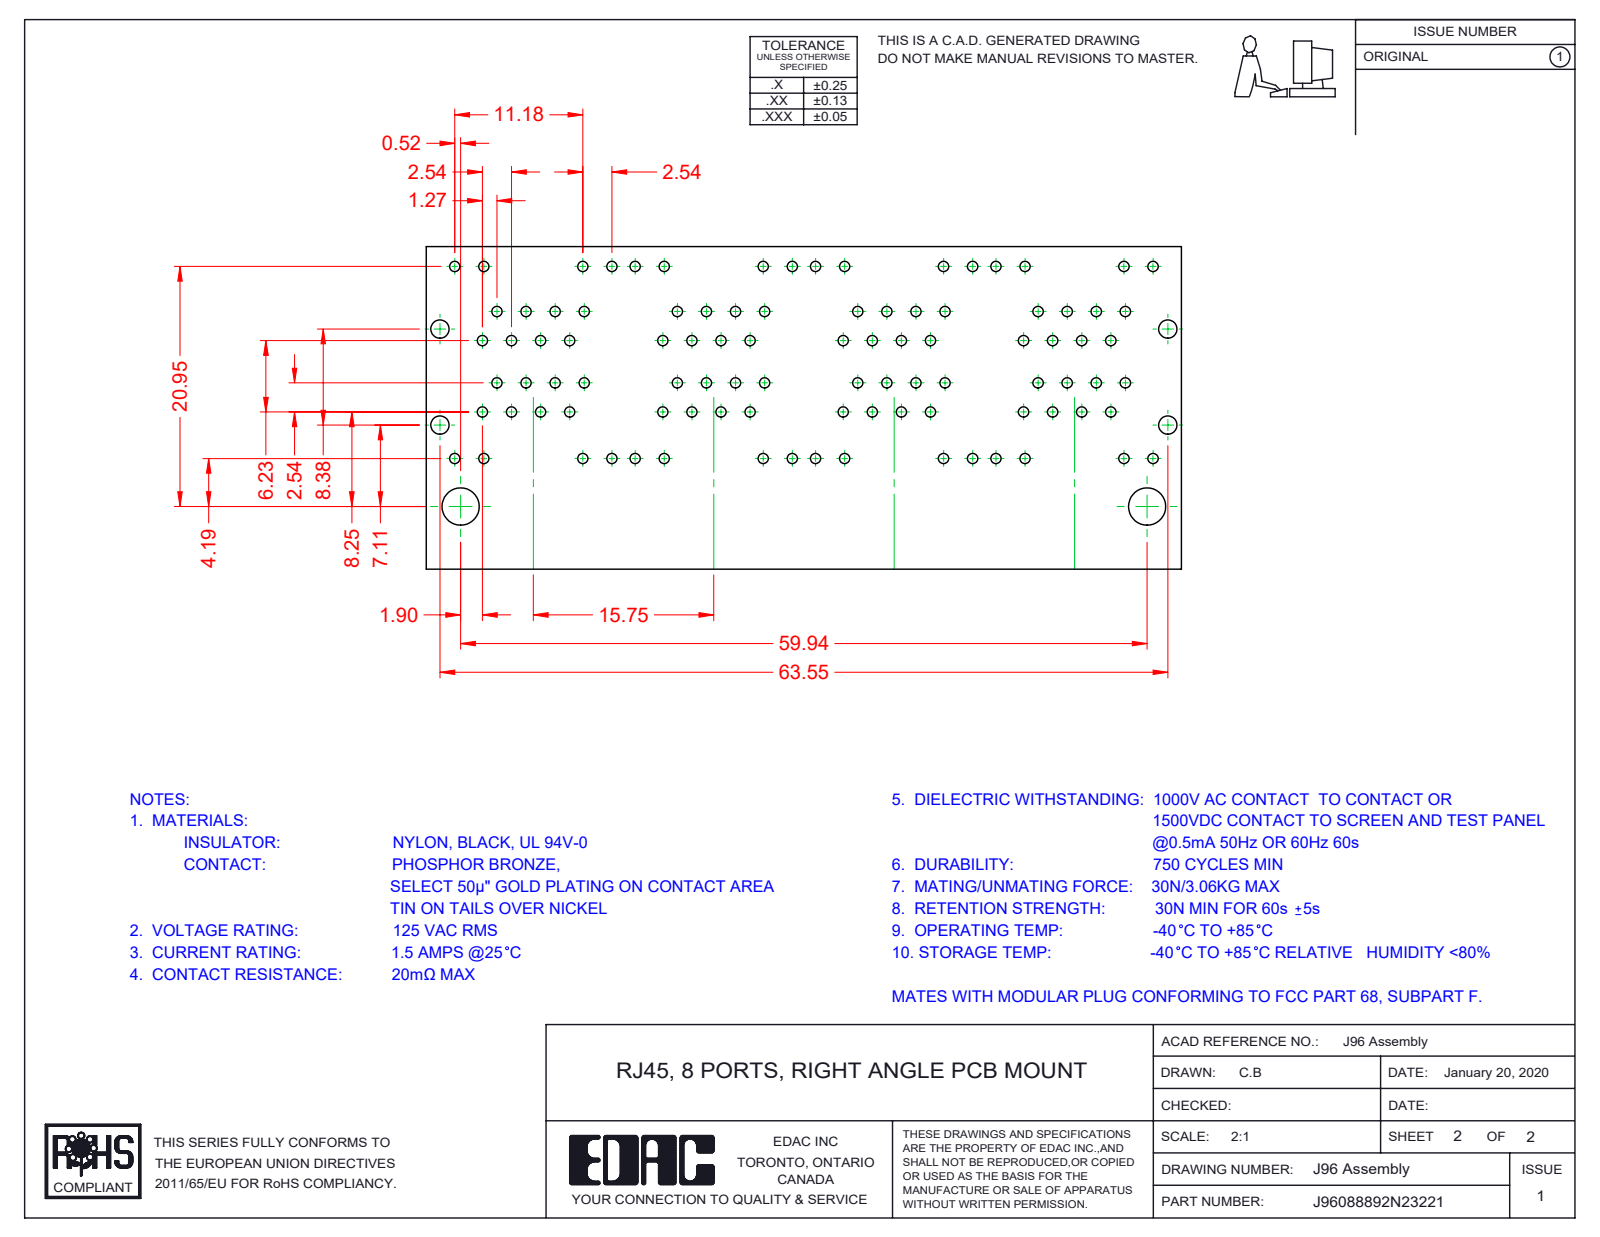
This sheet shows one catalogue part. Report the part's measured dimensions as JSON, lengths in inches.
{"part_name": "96 Grounding_8 Ports; 96 Insulator_8 Ports; 96 LED RH Upper_3-Green; J96088892N23221 (+8 more)", "step_written_by": "SolidWorks 2016 (CONFIG_CONTROL_DESIGN)", "units": "inches", "bodies": {"solids": 96, "faces": 7804, "planar": 6105, "cylindrical": 1388, "other": 311}, "overall_size": [2.652, 1.235, 1.129], "volume_in3": 1.474, "surface_area_in2": 98.57, "round_holes": [[0.067, 3]], "round_bosses_or_shafts": [[0.066, 3]], "partial_cylinders_radius": [[0.01, 124], [0.014, 73], [0.039, 72], [0.02, 49], [0.036, 32], [0.008, 27], [0.011, 14], [0.028, 11]], "face_to_face_distances": [0.62, 0.014, 0.392, 0.046, 0.063, 0.021, 0.393, 0.401, 0.499, 0.133], "hole_center_spacings": [0.62, 1.24]}
